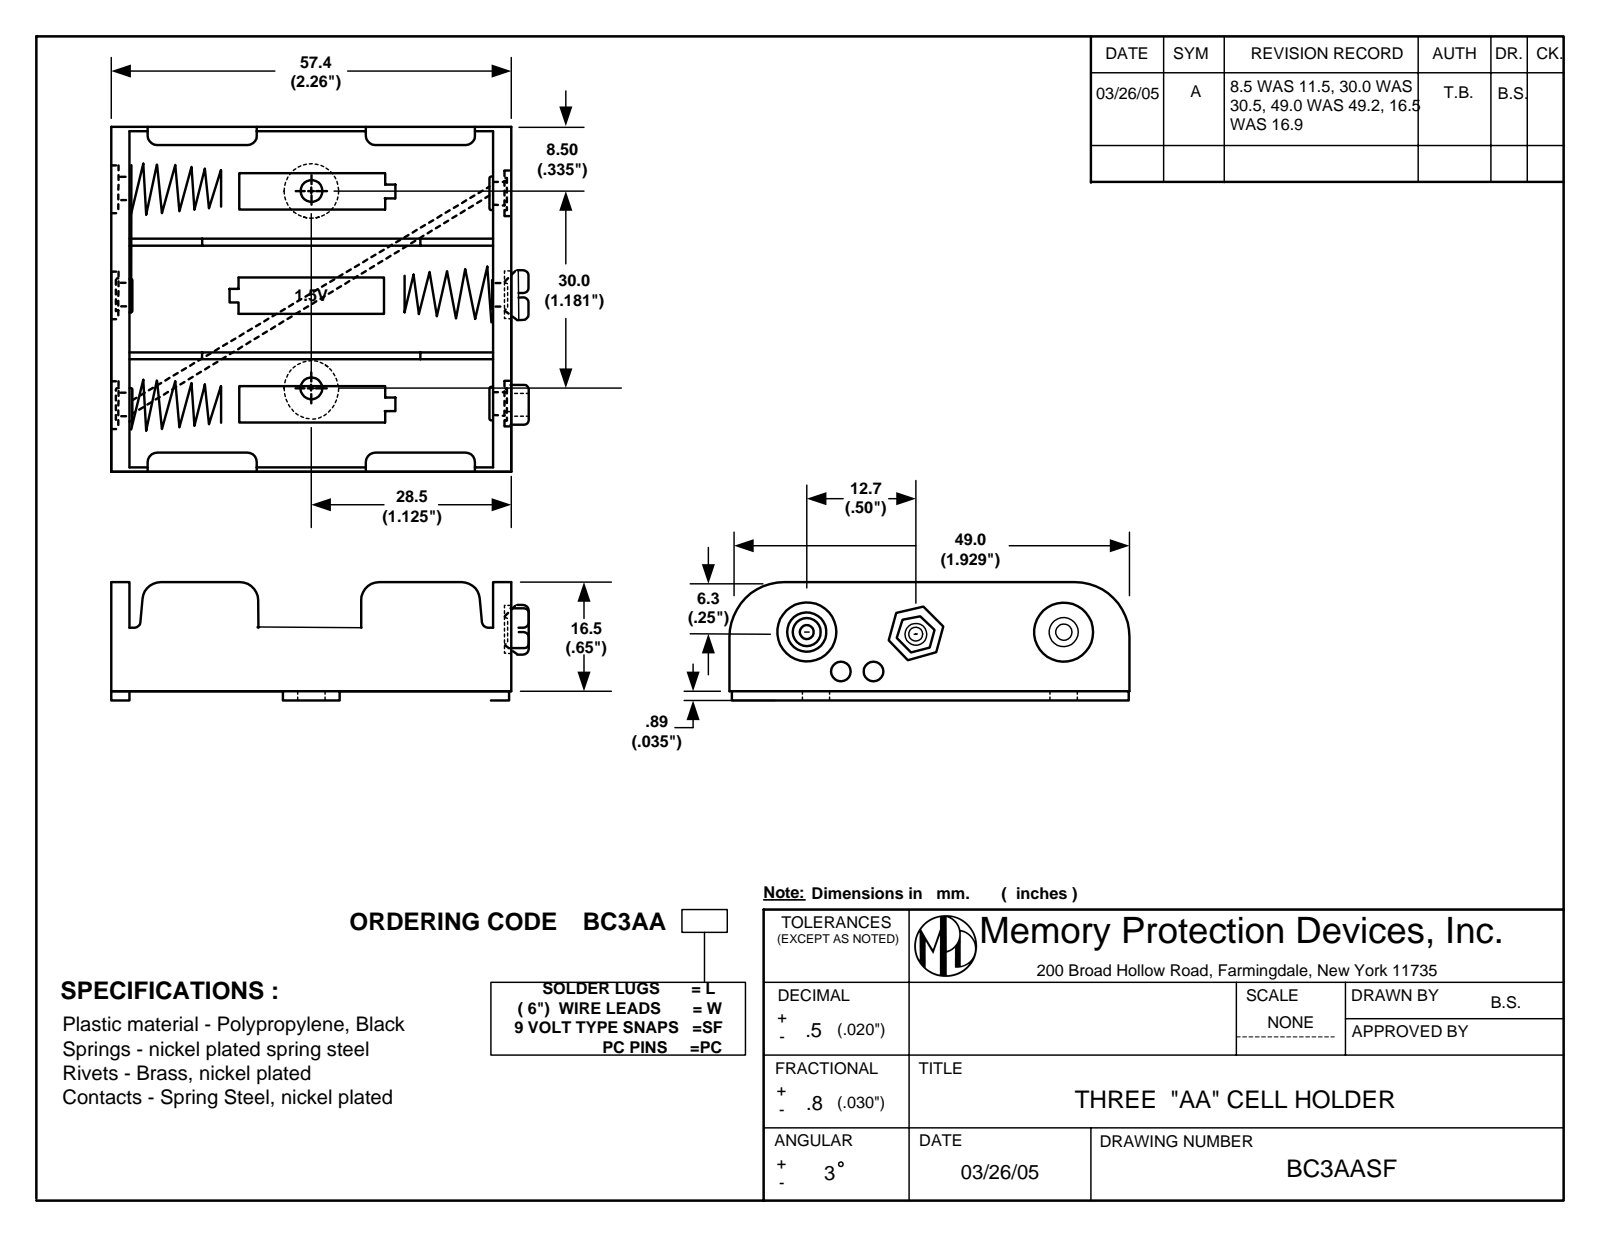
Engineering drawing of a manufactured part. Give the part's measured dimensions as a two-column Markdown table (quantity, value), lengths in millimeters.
| quantity | value |
| --- | --- |
| part name | BC3AASF |
| STEP written by | SolidWorks 2016 (AUTOMOTIVE_DESIGN) |
| units | millimeters |
| bodies | 8 solids, 515 faces (279 planar, 158 cylindrical, 78 other) |
| overall size | 61.19 × 49 × 16.5 |
| volume | 8 839 mm³ |
| surface area | 15 564 mm² |
| round holes (diameter × count) | 3.7 × 6, 2 × 5, 2.3 × 3, 3 × 3, 8 × 3, 3.1 × 2, 5 × 2, 4.95 × 1 |
| round bosses / shafts (diameter × count) | 4.7 × 6, 6.2 × 3, 3.5 × 3, 0.6 × 2, 7.92 × 1, 5.71 × 1, 0.7 × 1 |
| partial cylindrical surfaces (radius × count) | 2.5 × 8, 1.02 × 6, 4 × 3, 3.76 × 2, 4.1 × 2 |
| main face-to-face distances | 1.1, 1.55, 56.4, 47.9, 15.78, 16.33, 15.79, 32.11, 32.12, 55.3 |
| hole center spacings | 41.36, 16.33, 38, 8.34, 11.03, 16.34, 18.85, 19.25 |
